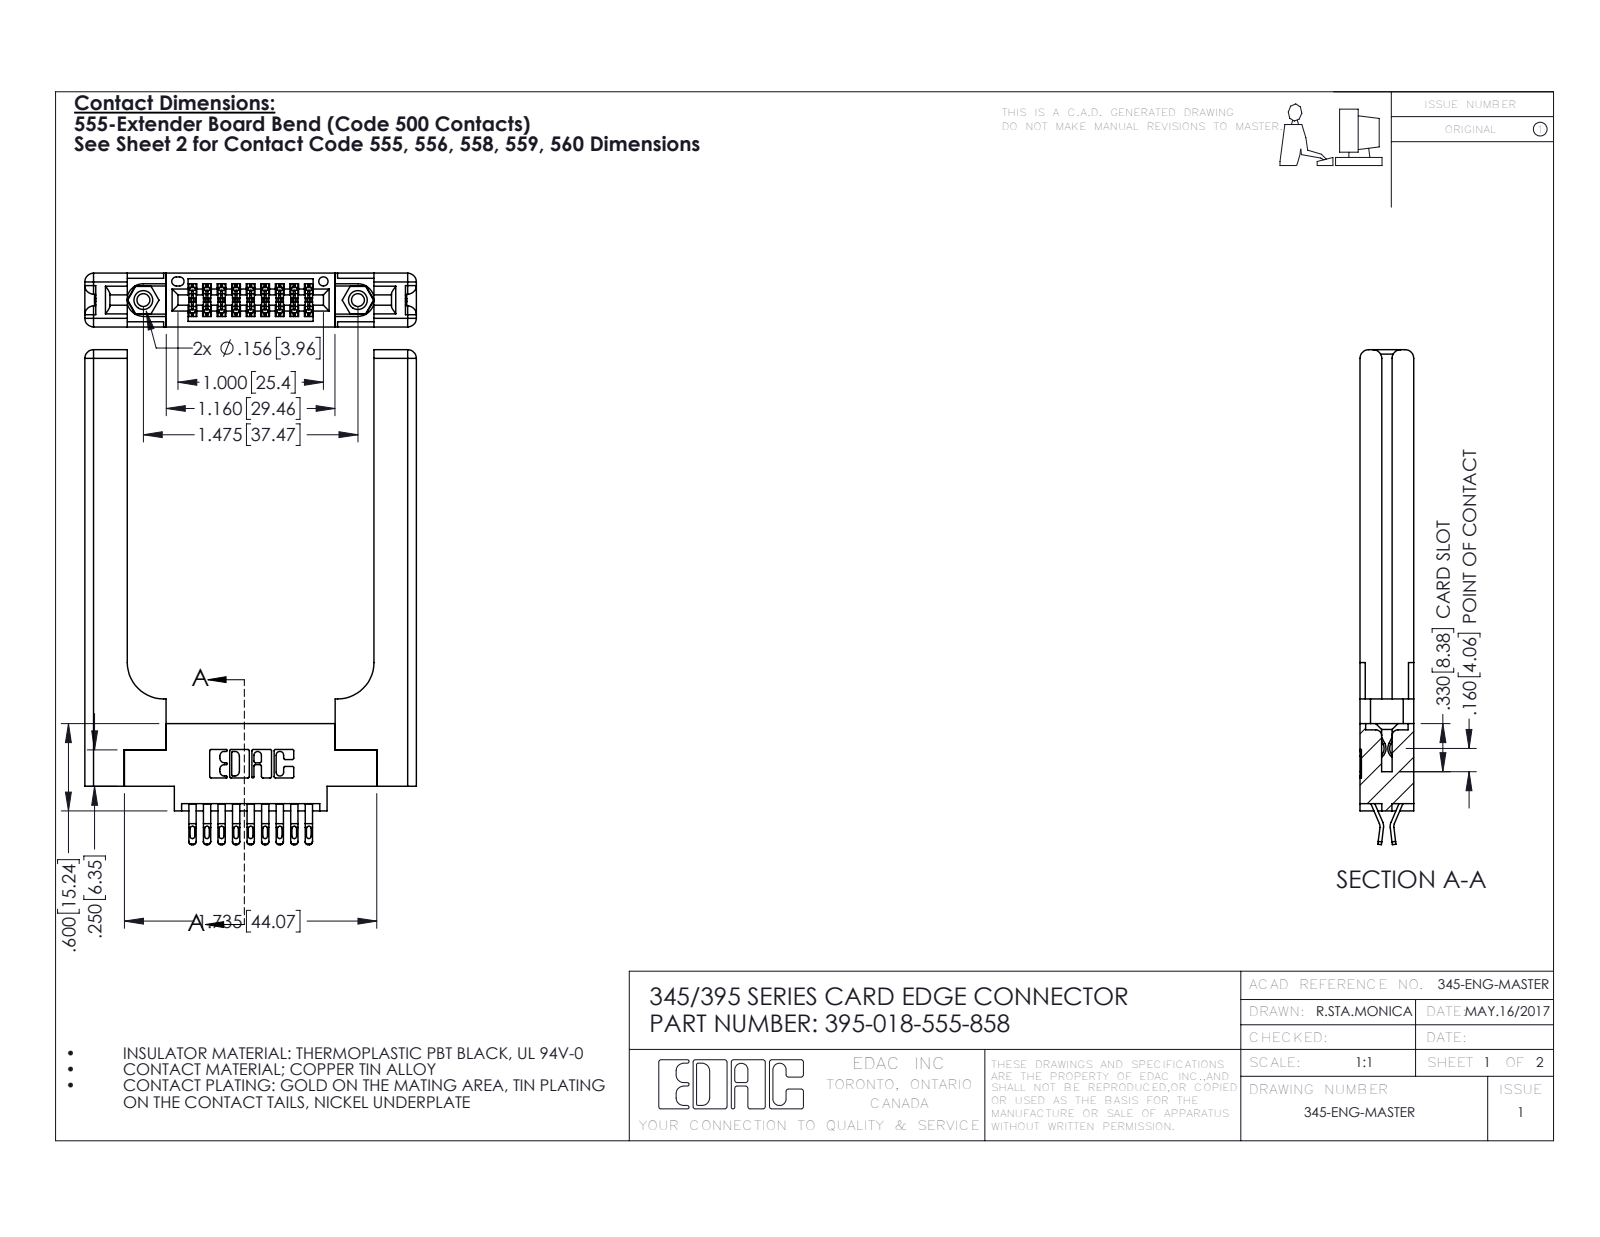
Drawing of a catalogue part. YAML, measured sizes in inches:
part_name: "395-018-555-858; 345-250-001_345-250-001-102; 345 Part_0.170 Offset - 0.156 Dia-TH; 345-220-058_345-220-058 (+1 more)"
step_written_by: "SolidWorks 2016 (CONFIG_CONTROL_DESIGN)"
units: inches
bodies: {solids: 23, faces: 1394, planar: 790, cylindrical: 544, other: 60}
overall_size: [3.402, 2.279, 0.37]
volume: 0.838
surface_area: 19.4
round_holes:
  - {diameter: 0.089, count: 2}
  - {diameter: 0.125, count: 2}
  - {diameter: 0.156, count: 2}
  - {diameter: 0.064, count: 1}
round_bosses_or_shafts:
  - {diameter: 0.155, count: 2}
partial_cylinders:
  - {radius: 0.016, count: 45}
  - {radius: 0.02, count: 36}
  - {radius: 0.006, count: 27}
  - {radius: 0.01, count: 22}
  - {radius: 0.06, count: 16}
  - {radius: 0.007, count: 6}
  - {radius: 0.031, count: 6}
  - {radius: 0.026, count: 3}
face_to_face_distances: [0.37, 0.15, 0.072, 0.22, 0.148, 0.077, 0.298, 1.696, 0.071, 0.225]
hole_center_spacings: [0.27, 1.244, 1.475]
